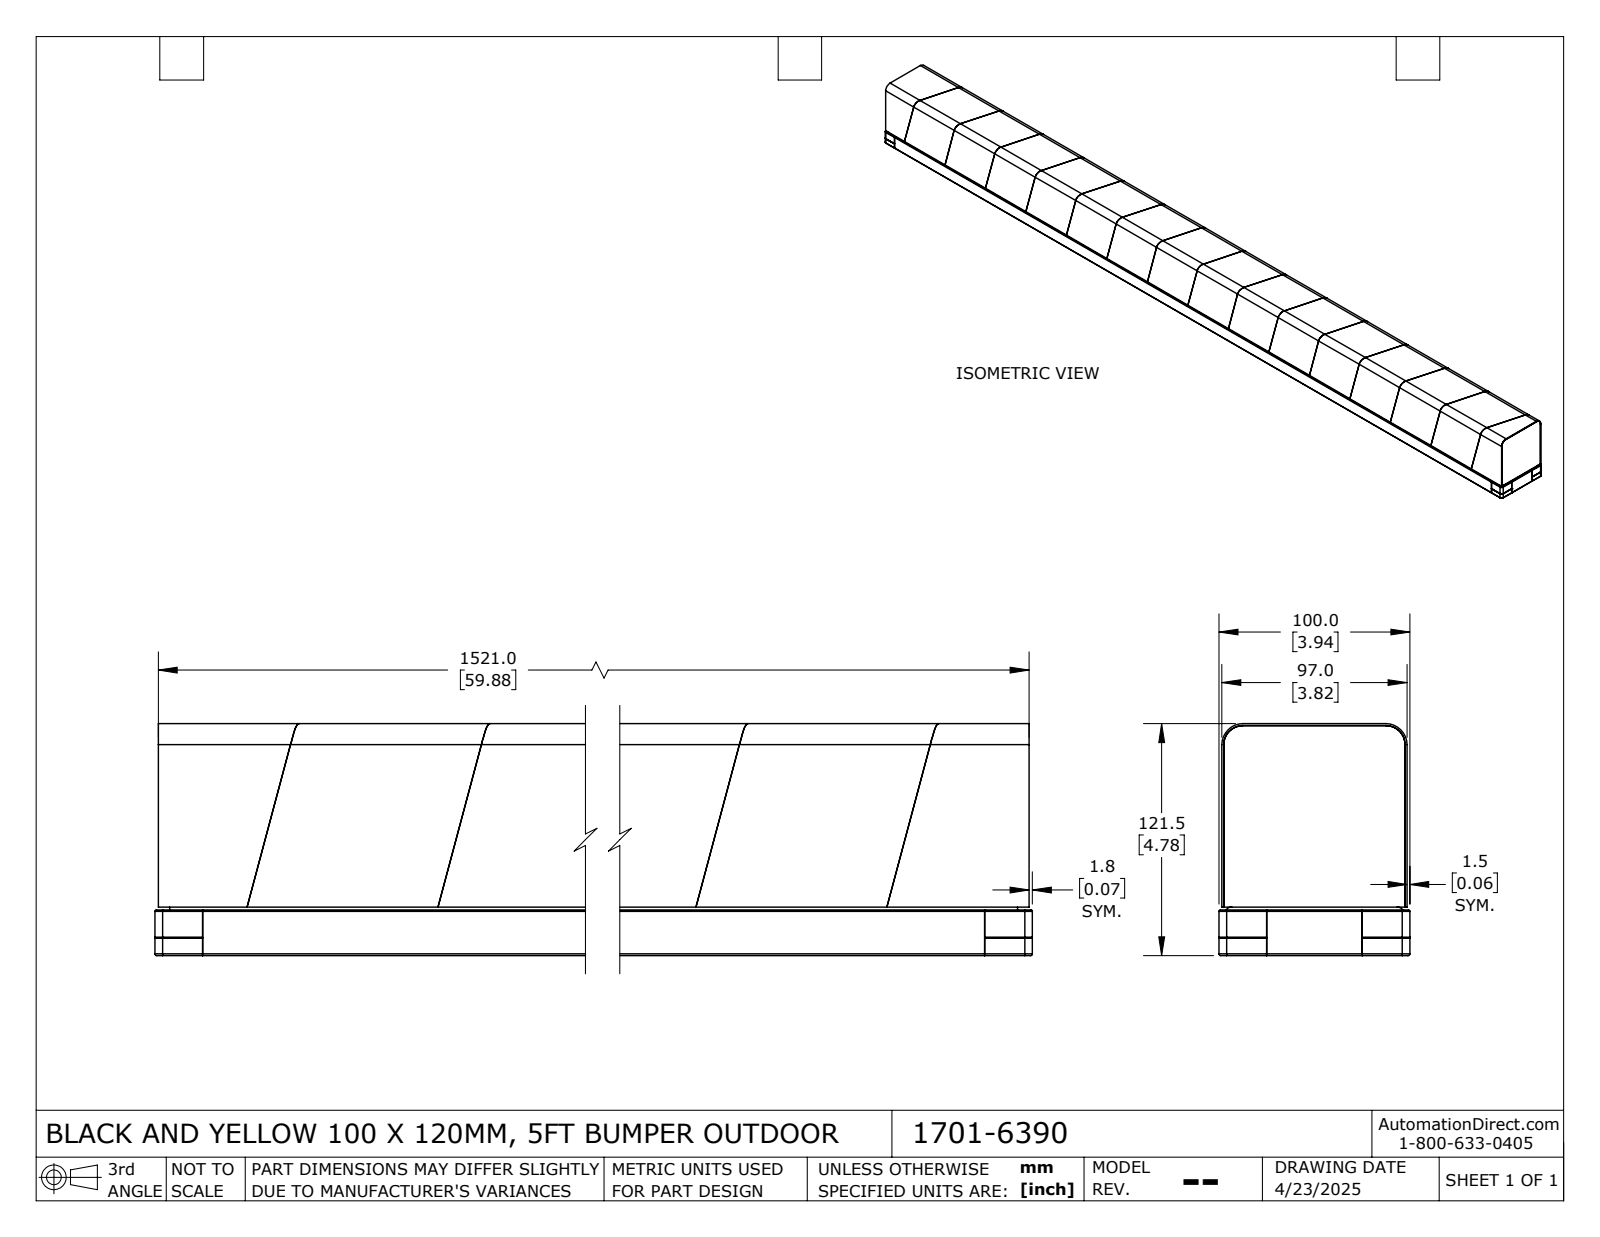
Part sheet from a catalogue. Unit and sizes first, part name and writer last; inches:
Units: inches
Overall size (bounding box): 60.02 × 4.783 × 3.937
Round holes (diameter × count): ⌀0.472 ×4
Partial cylindrical surfaces — rounded edges, fillets, slot ends (radius × count): R0.012 ×16, R0.02 ×8, R0.03 ×8, R0.039 ×8, R0.157 ×8, R0.079 ×4, R0.11 ×4, R0.236 ×4
Main face-to-face distances: 0.039, 3.74, 3.78, 0.079, 3.819, 0.925, 1.004, 4.744, 4.665, 3.642
Hole centre spacings: 19.219, 38.438, 19.219, 57.657
Volume: 923.1 in³ · Surface area: 3 919 in²
Bodies: 32 solids, 697 faces (417 planar, 188 cylindrical, 92 other)
Part name (STEP PRODUCT): 1701-6390 AD SENTIR bumper 100-120 LO 2_5 ft
STEP written by: SolidWorks 2024 (AUTOMOTIVE_DESIGN)
